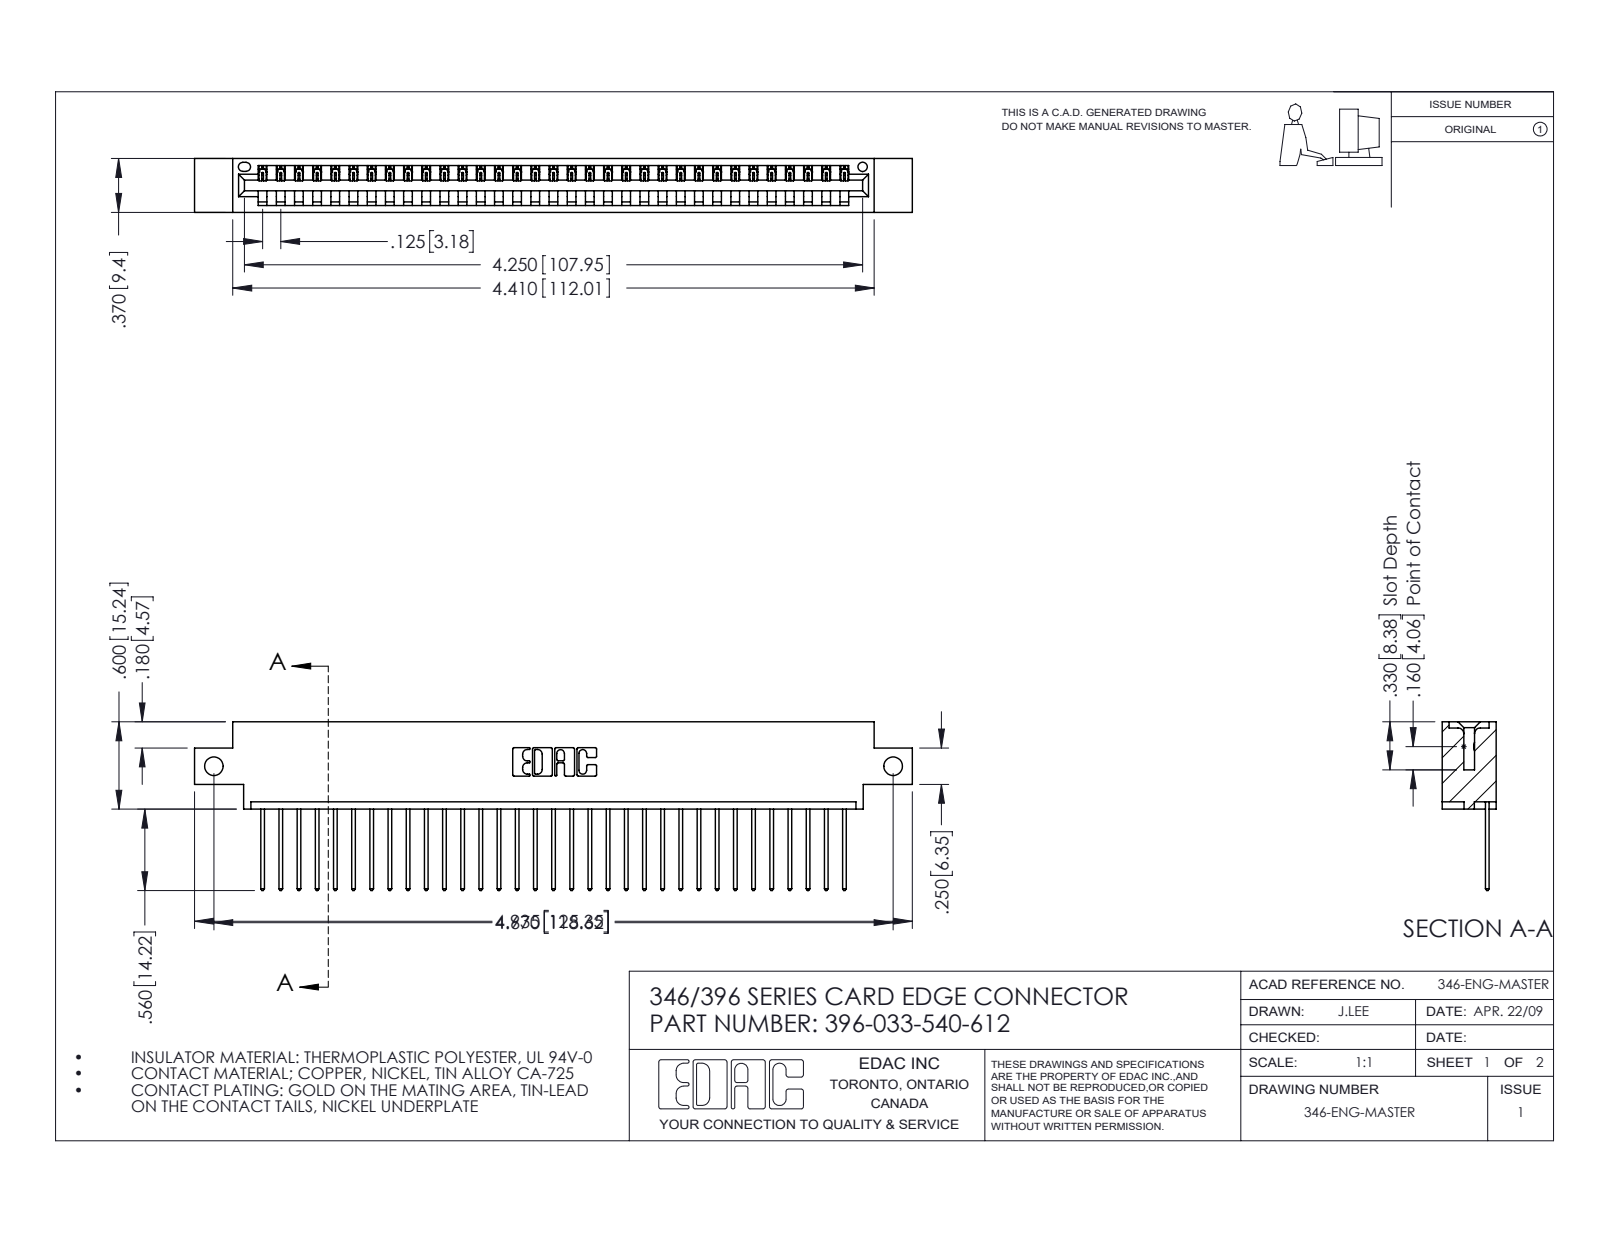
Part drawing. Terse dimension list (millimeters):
name: 346 Part_0.170 Offset - Side Mount; 396-033-540-612; 345-292-001_345-293-140
written by: SolidWorks 2016 (CONFIG_CONTROL_DESIGN)
unit: mm
bodies: 34 solids, 2040 faces (1400 planar, 640 cylindrical, 0 other)
size: 125.3 × 29.5 × 9.4
volume: 11 700 mm³; area: 14 920 mm²
holes: 2× ⌀3.3, 1× ⌀1.6
rounds: 66× R0.2, 66× R0.3, 22× R0.3, 6× R0.2, 6× R0.8, 3× R0.7, 2× R0.8, 2× R1
face distances: 1.2, 8.2, 9.4, 6.4, 1.8, 7.6, 0.6, 3.8, 5.6, 2.5
hole spacings: 118.6
